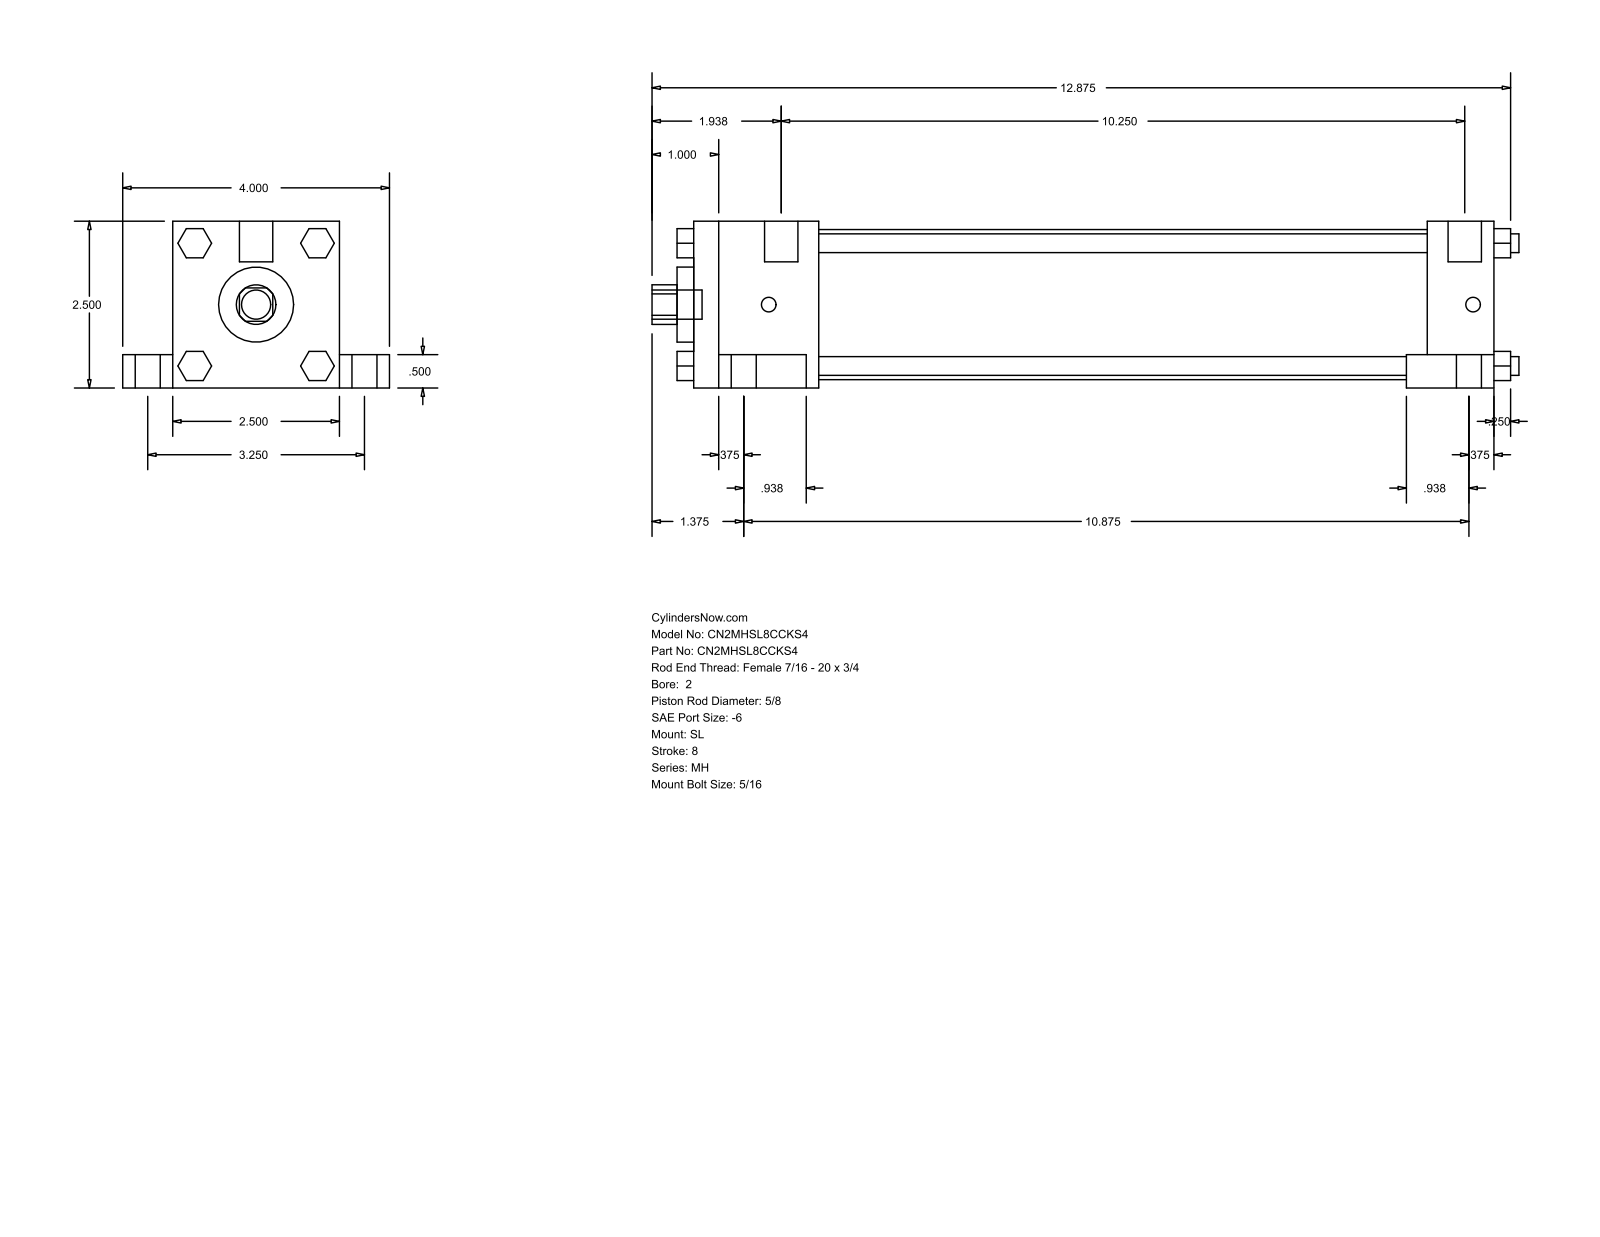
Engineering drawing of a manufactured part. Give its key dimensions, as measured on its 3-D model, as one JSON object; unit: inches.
{"part_name": "MH_SL__0200_0.625", "step_written_by": "GSSL Pune (CONFIG_CONTROL_DESIGN)", "units": "inches", "bodies": {"solids": 0, "faces": 148, "planar": 112, "cylindrical": 36, "other": 0}, "overall_size": [13, 4, 2.5], "round_holes": [[0.625, 1], [1.125, 1], [2.25, 1]], "round_bosses_or_shafts": [[0.625, 4], [0.375, 4], [0.281, 4], [0.219, 4], [0.5, 2], [0.437, 1]], "partial_cylinders_radius": [[0.297, 1]], "face_to_face_distances": [2.5, 12, 0.5, 0.75, 2, 3.25, 11, 1, 1.875, 9.125]}
